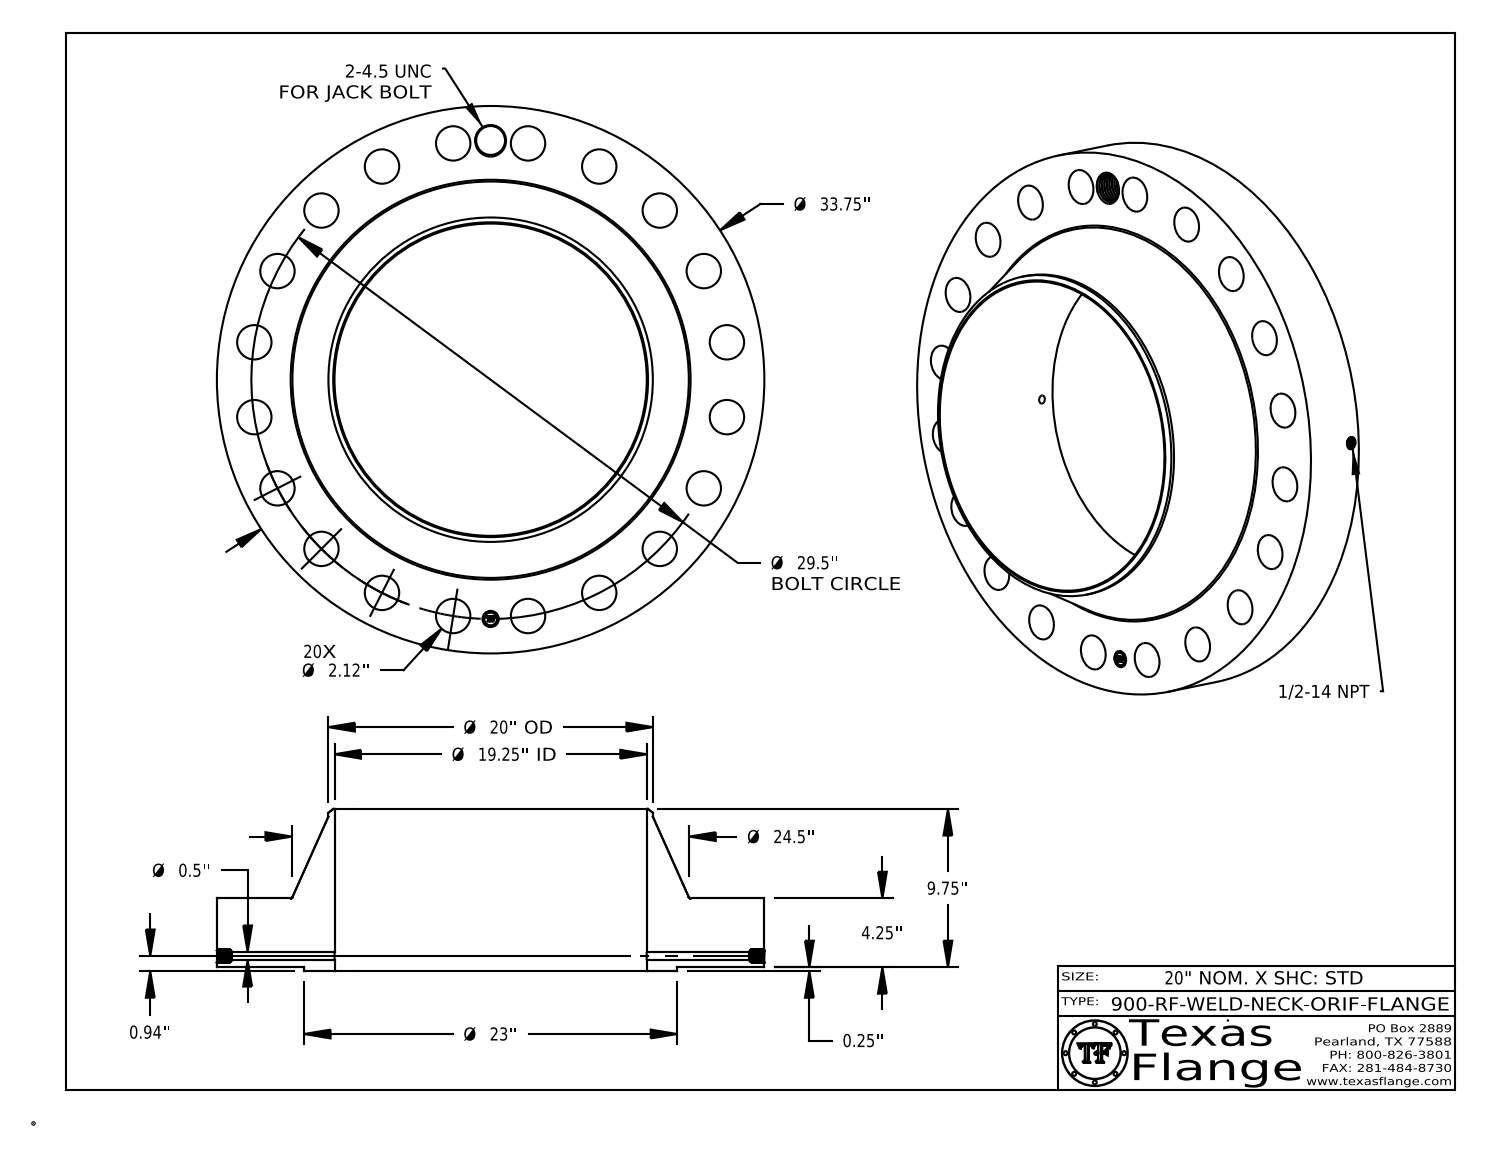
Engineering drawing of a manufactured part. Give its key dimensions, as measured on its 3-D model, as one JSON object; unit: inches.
{"part_name": "900-RF-WELD-NECK", "step_written_by": "CATIA V5 STEP AP214 (AUTOMOTIVE_DESIGN)", "units": "inches", "bodies": {"solids": 1, "faces": 818, "planar": 369, "cylindrical": 126, "other": 323}, "overall_size": [33.75, 33.75, 10], "volume_in3": 2789, "surface_area_in2": 3008, "round_holes": [[2.12, 20], [0.5, 1], [0.672, 1], [1, 1], [1.781, 1], [19.25, 1]], "round_bosses_or_shafts": [[0.061, 8], [33.75, 1], [23, 1], [20, 1], [0.788, 1]], "face_to_face_distances": [4.25, 0.25, 4.5, 10, 9.75, 5.5, 4.485, 4.235, 0.015, 5.515], "hole_center_spacings": [4.615, 9.116, 13.393, 17.34, 20.86, 23.866, 26.285, 29.137]}
